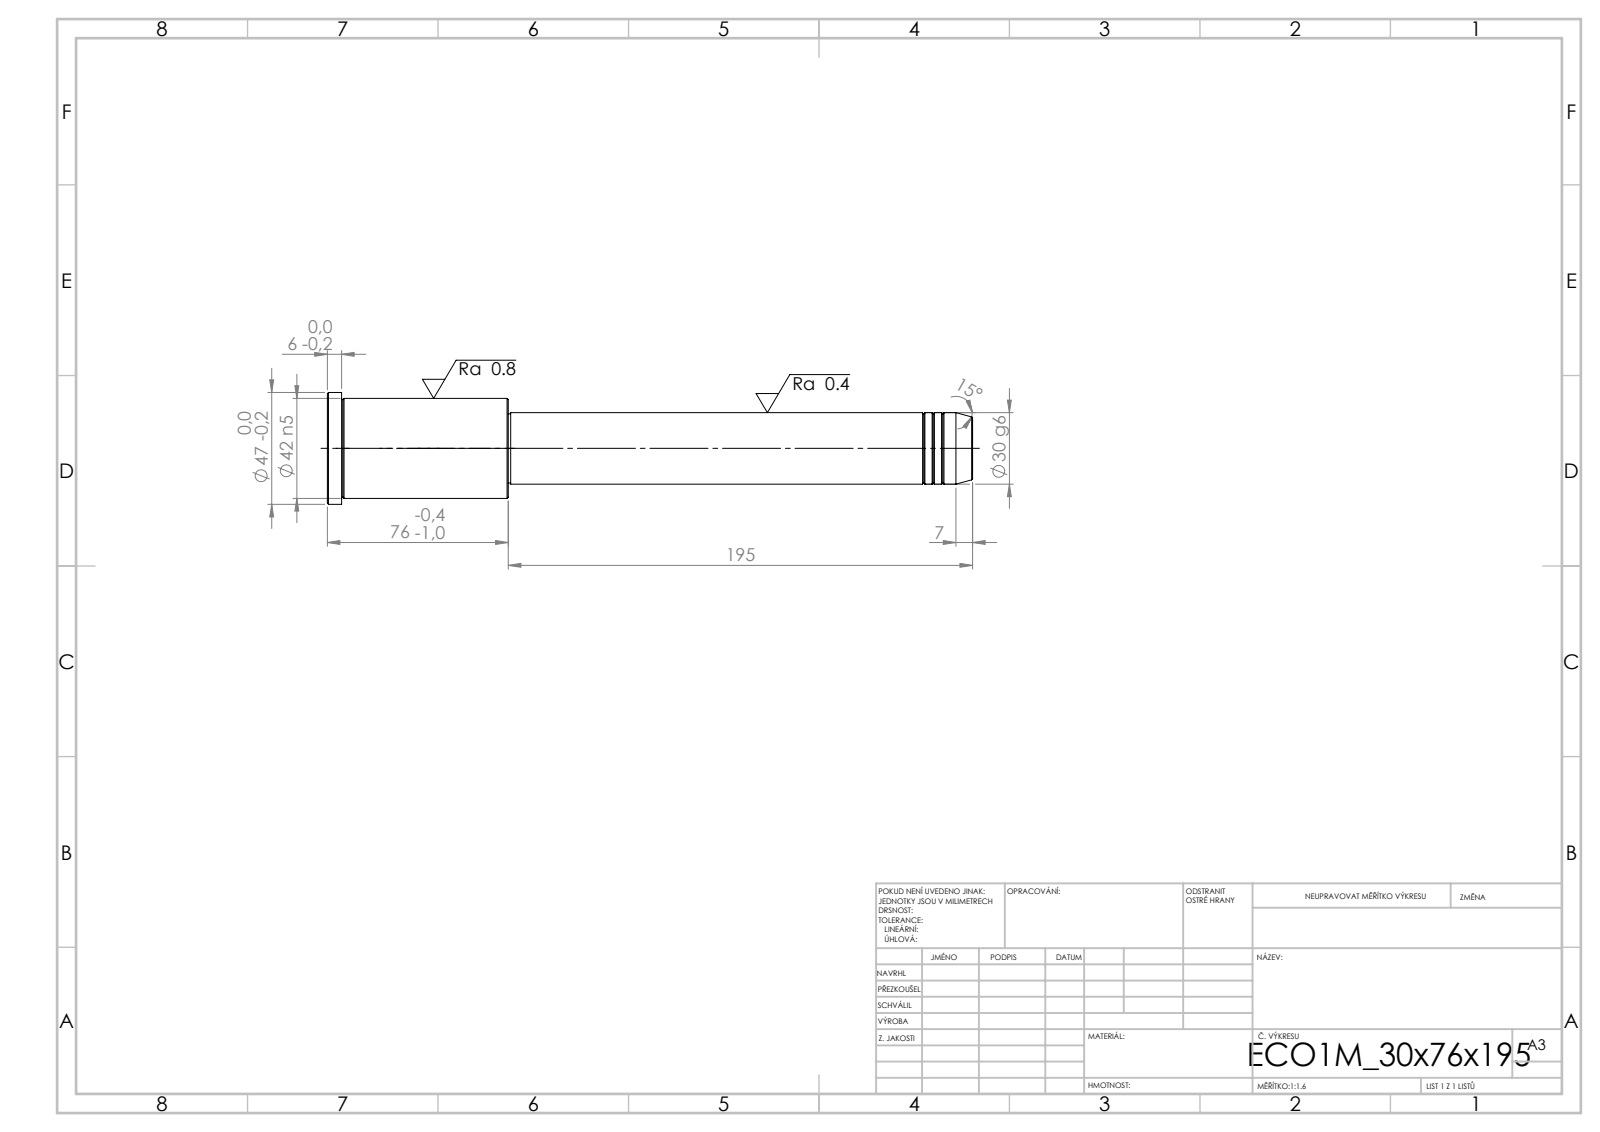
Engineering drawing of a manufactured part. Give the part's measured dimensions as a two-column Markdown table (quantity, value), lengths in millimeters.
| quantity | value |
| --- | --- |
| STEP written by | SolidWorks 2019 (CONFIG_CONTROL_DESIGN) |
| units | millimeters |
| bodies | 1 solid, 43 faces (5 planar, 14 cylindrical, 24 other) |
| overall size | 271 × 47 × 47 |
| volume | 244 391 mm³ |
| surface area | 32 007 mm² |
| round bosses / shafts (diameter × count) | 47 × 1, 42 × 1, 30 × 1, 29 × 1 |
| main face-to-face distances | 76, 195, 271, 265, 70, 6, 194, 1, 71, 77 |
